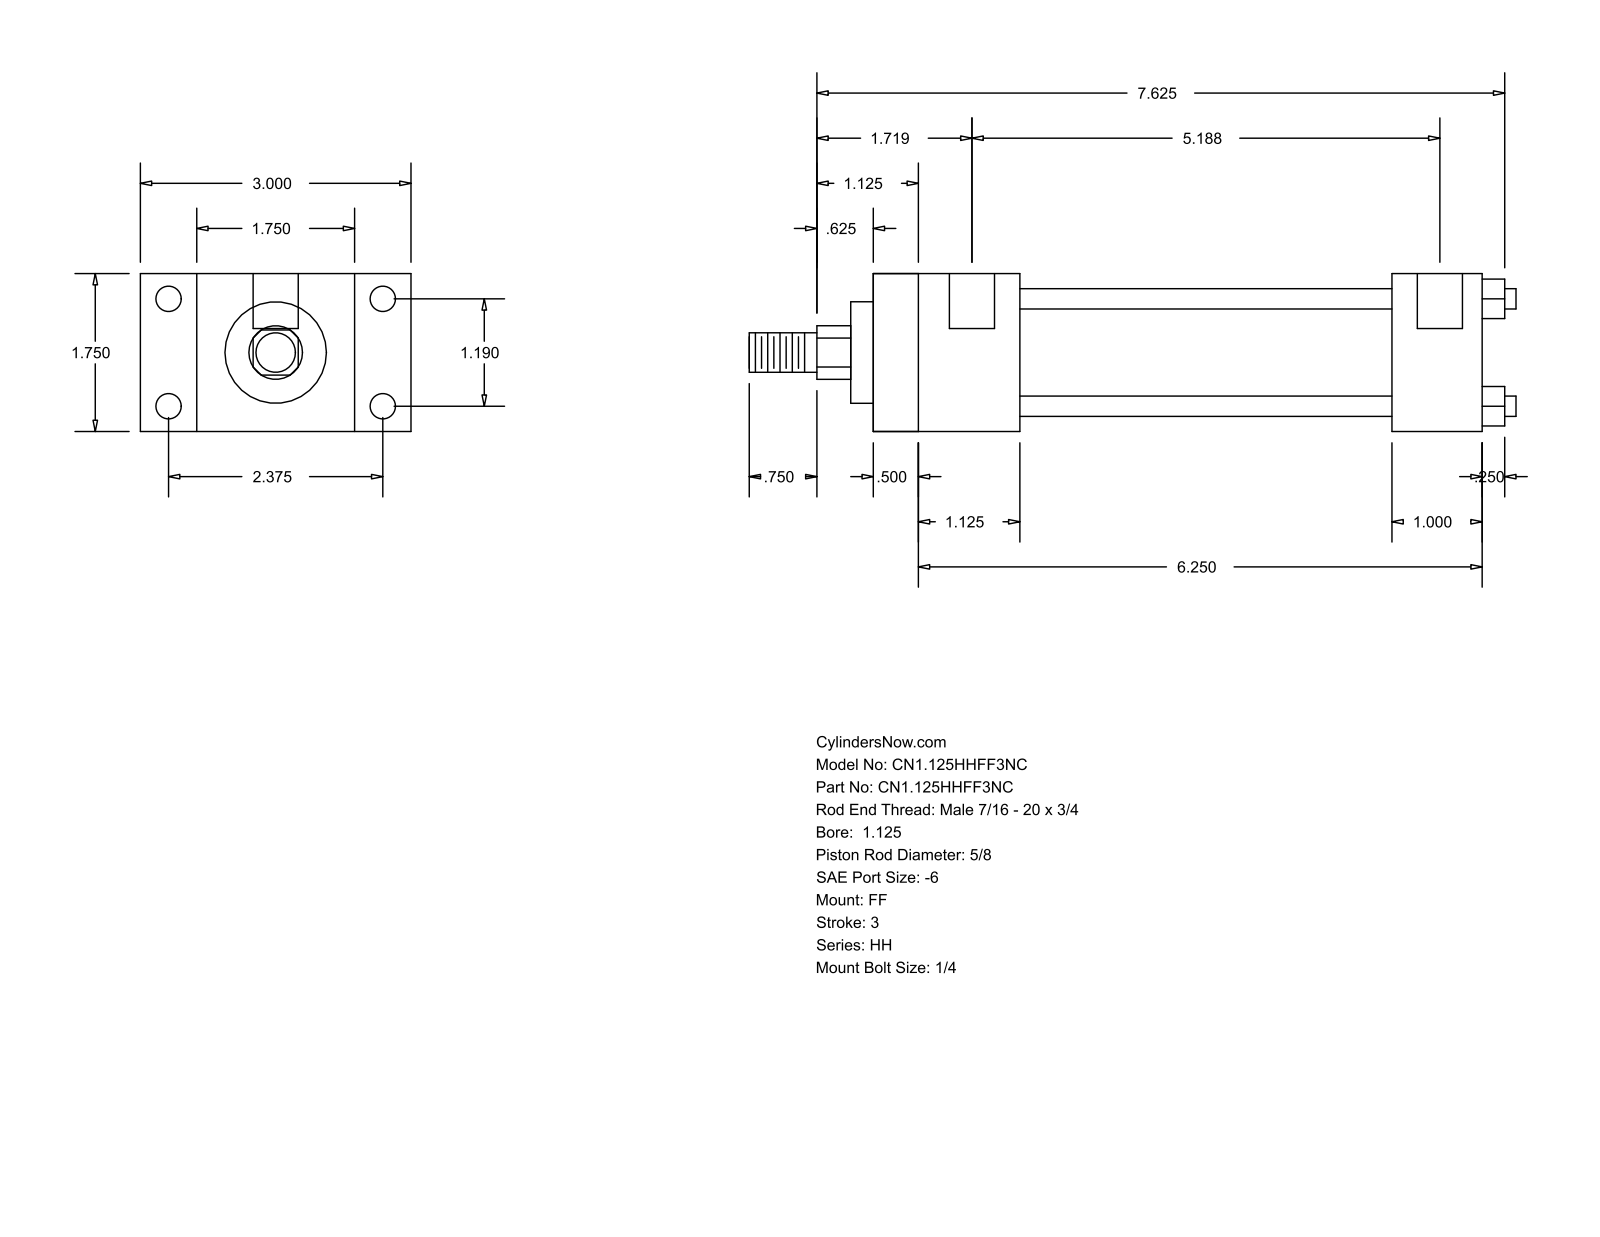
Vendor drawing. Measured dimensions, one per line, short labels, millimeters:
name: HH_FF__0112_0.625
written by: GSSL Pune (CONFIG_CONTROL_DESIGN)
unit: mm
bodies: 0 solids, 92 faces (64 planar, 28 cylindrical, 0 other)
size: 215.9 × 76.2 × 44.45
holes: 4× ⌀5.56, 4× ⌀7.14, 2× ⌀12.7
bosses: 4× ⌀5.71, 1× ⌀34.92, 1× ⌀28.57, 1× ⌀15.88, 1× ⌀11.11
rounds: 1× R7.54
face distances: 44.46, 171.44, 15.87, 12.69, 158.75, 28.58, 60.33, 41.27, 146.05, 133.36
hole spacings: 30.22, 60.32, 67.47, 128.59, 3.17, 131.76
